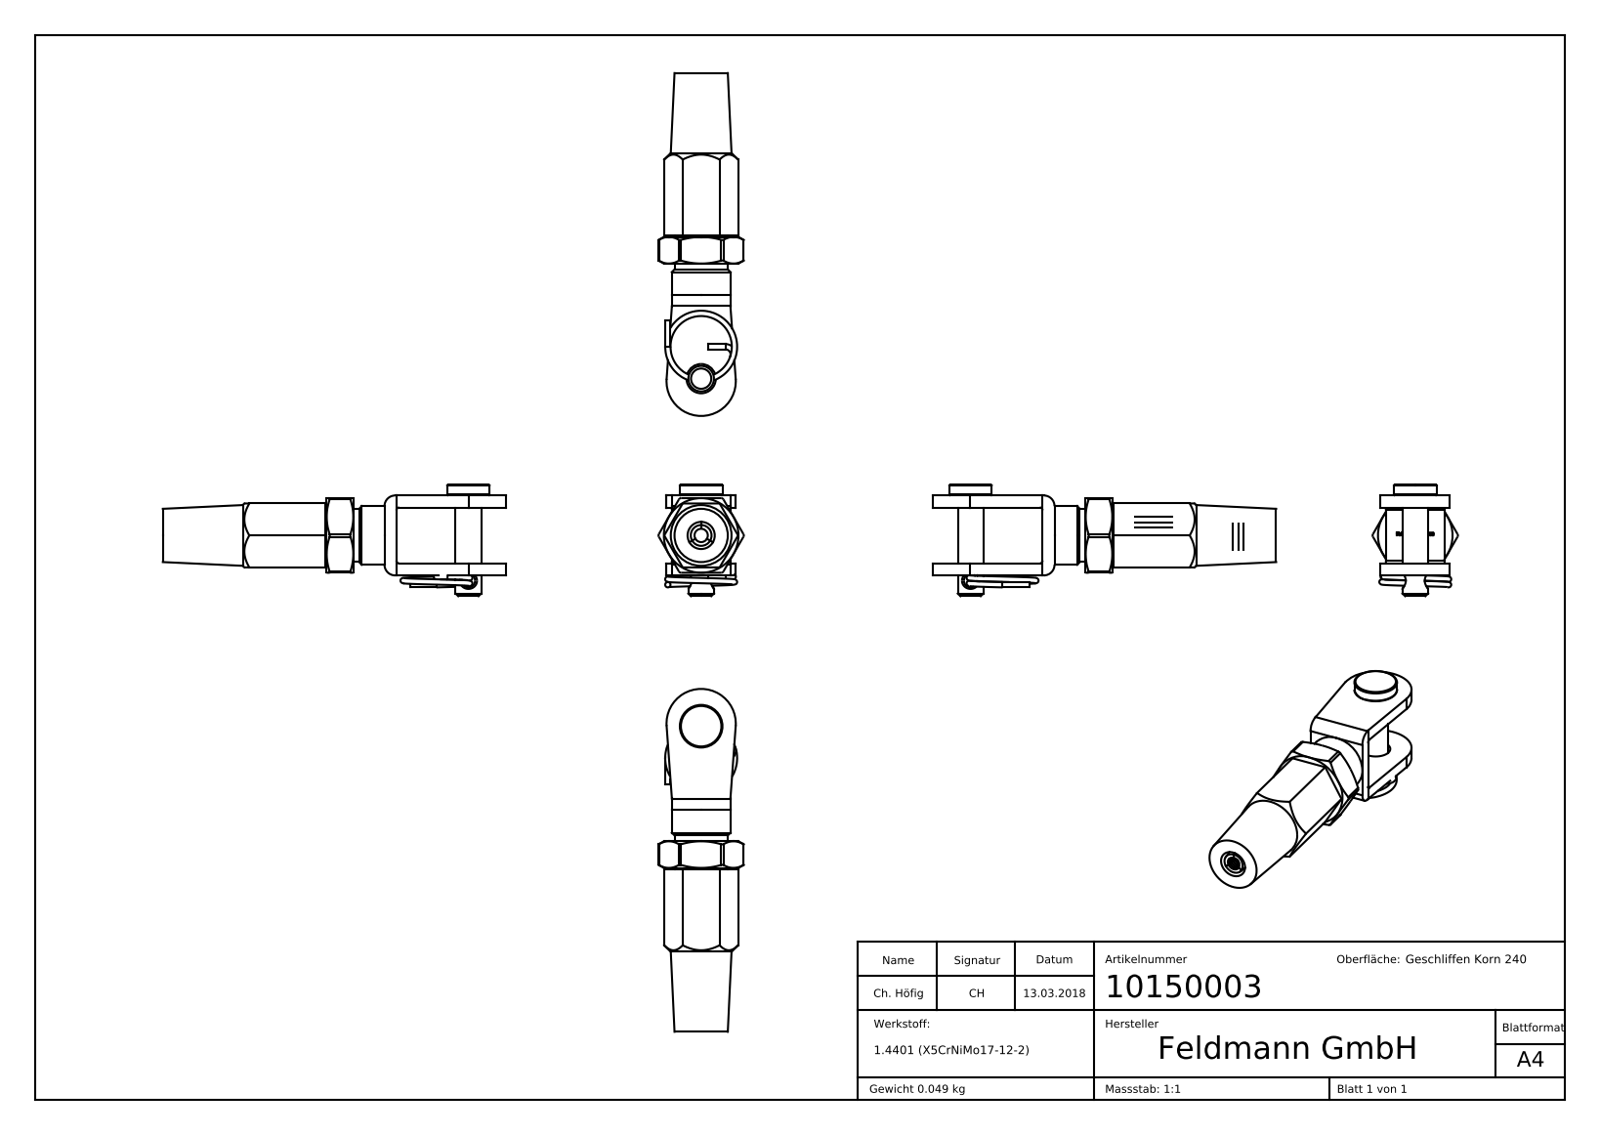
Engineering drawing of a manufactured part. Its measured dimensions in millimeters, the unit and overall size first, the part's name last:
Units: millimetres
Overall size (bounding box): 64.35 × 20.9 × 16.01
Round holes (diameter × count): ⌀2.5 ×2, ⌀4 ×1, ⌀4.05 ×1, ⌀5.5 ×1, ⌀5.76 ×1, ⌀8.5 ×1
Round bosses / shafts (diameter × count): ⌀8 ×2, ⌀1 ×2, ⌀11 ×1, ⌀10 ×1, ⌀4.8 ×1
Partial cylindrical surfaces — rounded edges, fillets, slot ends (radius × count): R0.5 ×8, R2 ×2, R6.5 ×1
Main face-to-face distances: 2.25, 12.75, 12, 15, 13, 1, 1.5, 13.5, 0.75, 11.25
Volume: 6 109 mm³ · Surface area: 6 209 mm²
Bodies: 10 solids, 517 faces (150 planar, 118 cylindrical, 249 other)
Part name (STEP PRODUCT): 10150003; 1015000X Teil3_10150003 Teil3; 1015000X Teil4_10150003 Teil4; 1015000X Teil8_10150003 Teil7 (+5 more)
STEP written by: SolidWorks 2015 (CONFIG_CONTROL_DESIGN)
